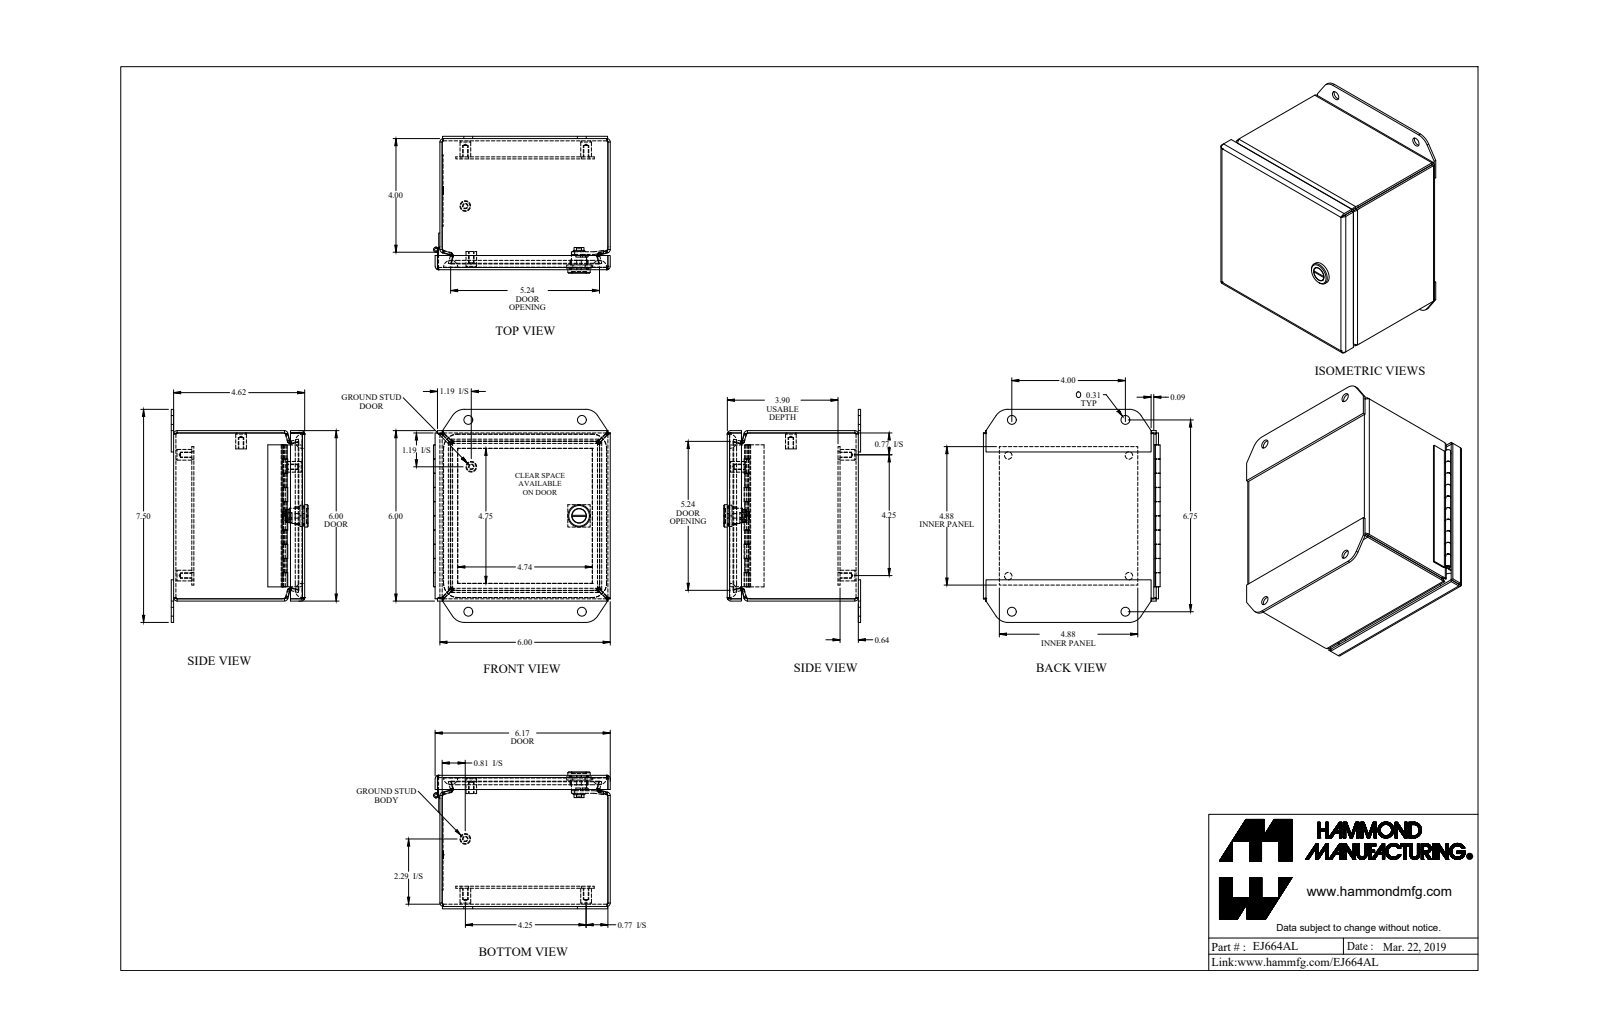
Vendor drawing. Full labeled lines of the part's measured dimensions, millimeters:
Part name (STEP PRODUCT): EJ664AL_Default
STEP written by: SolidWorks 2019 (CONFIG_CONTROL_DESIGN)
Units: millimetres
Bodies: 14 solids, 550 faces (330 planar, 152 cylindrical, 68 other)
Overall size (bounding box): 190.5 × 158.1 × 122.4
Volume: 344 600 mm³ · Surface area: 346 300 mm²
Round holes (diameter × count): ⌀4 ×6, ⌀6.7 ×4, ⌀8 ×4, ⌀13.1 ×1
Round bosses / shafts (diameter × count): ⌀9.5 ×6, ⌀8.4 ×6, ⌀20 ×1, ⌀13.6 ×1, ⌀12.6 ×1, ⌀11 ×1, ⌀4.6 ×1, ⌀2.5 ×1
Partial cylindrical surfaces — rounded edges, fillets, slot ends (radius × count): R1 ×16, R3.1 ×16, R7.1 ×12, R6.4 ×4, R12.7 ×4, R12.7 ×4, R1.5 ×2, R0.8 ×1
Main face-to-face distances: 2.1, 150.3, 115.2, 117.3, 152.4, 148.3, 113.2, 16.3, 14.3, 100.9
Hole centre spacings: 108, 152.7, 0.9, 31.9, 107.3, 139.8, 54.3, 85.8
